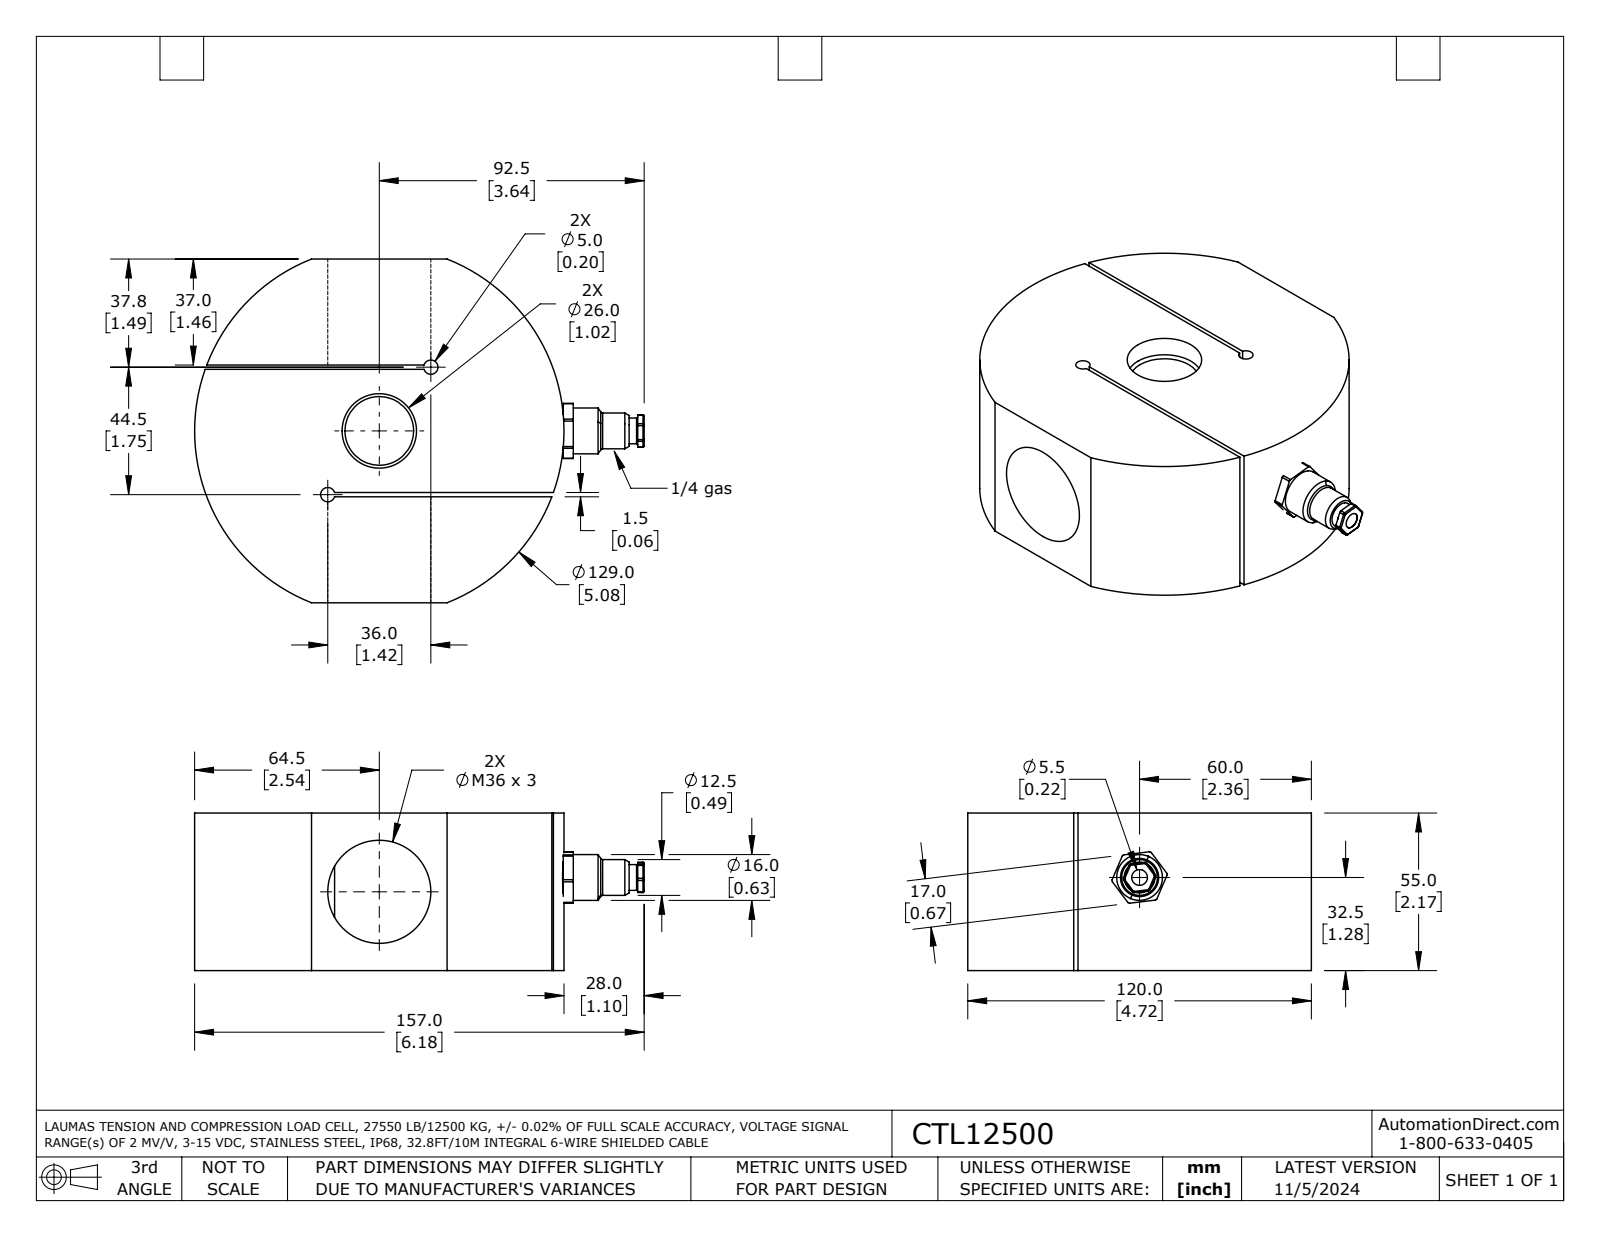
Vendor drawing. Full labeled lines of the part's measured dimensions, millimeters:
Part name (STEP PRODUCT): CTL12500
STEP written by: SolidWorks 2021 (AUTOMOTIVE_DESIGN)
Units: millimetres
Bodies: 2 solids, 100 faces (31 planar, 50 cylindrical, 19 other)
Overall size (bounding box): 157 × 120 × 55
Volume: 607 100 mm³ · Surface area: 73 100 mm²
Round holes (diameter × count): ⌀5 ×2, ⌀5.5 ×1, ⌀14 ×1, ⌀26 ×1, ⌀36 ×1
Round bosses / shafts (diameter × count): ⌀16 ×1, ⌀12.5 ×1, ⌀9 ×1
Partial cylindrical surfaces — rounded edges, fillets, slot ends (radius × count): R0.8 ×12, R0.4 ×6, R64.5 ×1
Main face-to-face distances: 55, 1.5, 44.5, 43, 46, 37, 38.5, 81.5, 83, 120
Hole centre spacings: 28.6, 57.3
